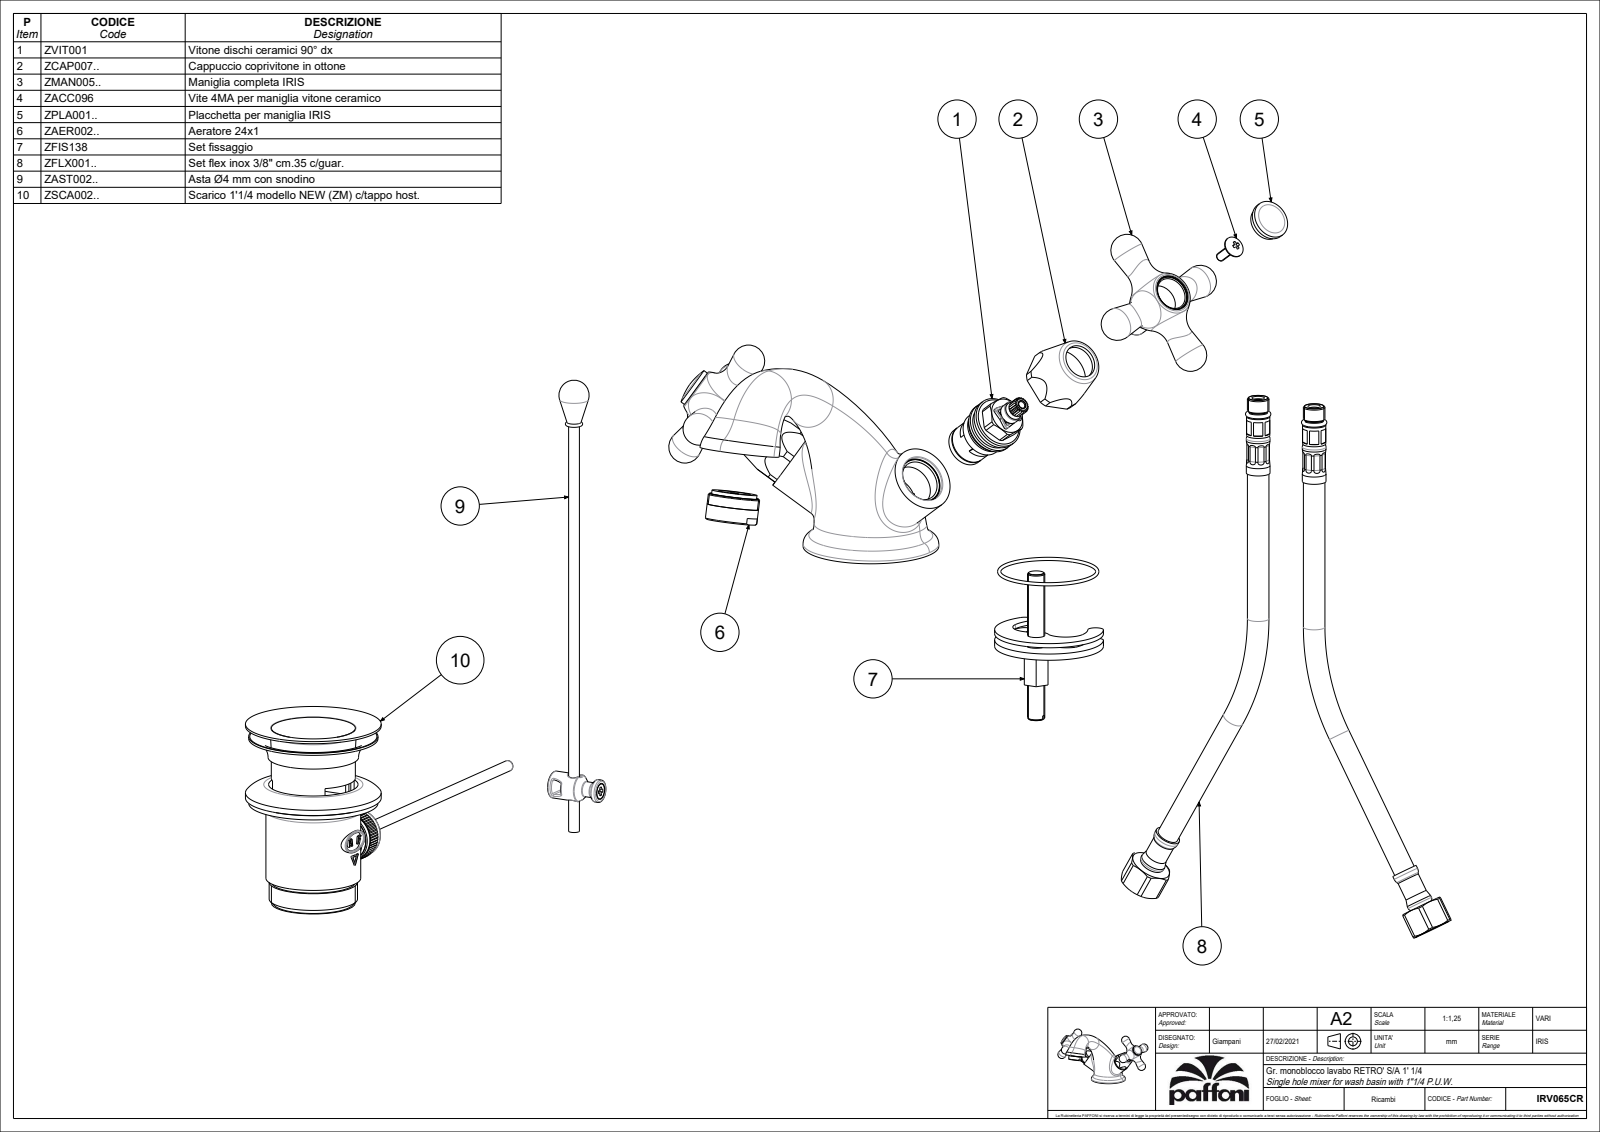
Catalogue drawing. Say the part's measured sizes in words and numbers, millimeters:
The part is named "IRV065CR". Its 3-D file was written by "CREO PARAMETRIC BY PTC INC, 2020044 (CONFIG_CONTROL_DESIGN)". It is 1 solid with 325 faces: 82 planar, 73 cylindrical and 170 other. Overall it measures 185.61 by 171.45 by 106.41 millimeters. Its volume is 180 371 cubic millimeters and its surface area 64 901 square millimeters. Round holes: 4 of diameter 9, 3 of diameter 21, 2 of diameter 11, 2 of diameter 19, 2 of diameter 21.5, 1 of diameter 5.5, 1 of diameter 6.8, 1 of diameter 16.5, 1 of diameter 20, 1 of diameter 23, 1 of diameter 49. Round bosses or shafts: 2 of diameter 28, 2 of diameter 18, 2 of diameter 13.5, 1 of diameter 63, 1 of diameter 44, 1 of diameter 24. Partial cylindrical surfaces (rounded edges, fillets, slot ends): 2 of radius 14.5, 1 of radius 5. The main face-to-face distances are 21.91, 7.7, 1.3, 8.5, 7.8, 26.51, 19.01, 6, 24.1, 46.01. The hole center spacings are 7.5, 12.66, 13.48, 10.2, 11.2, 15, 21.4.
